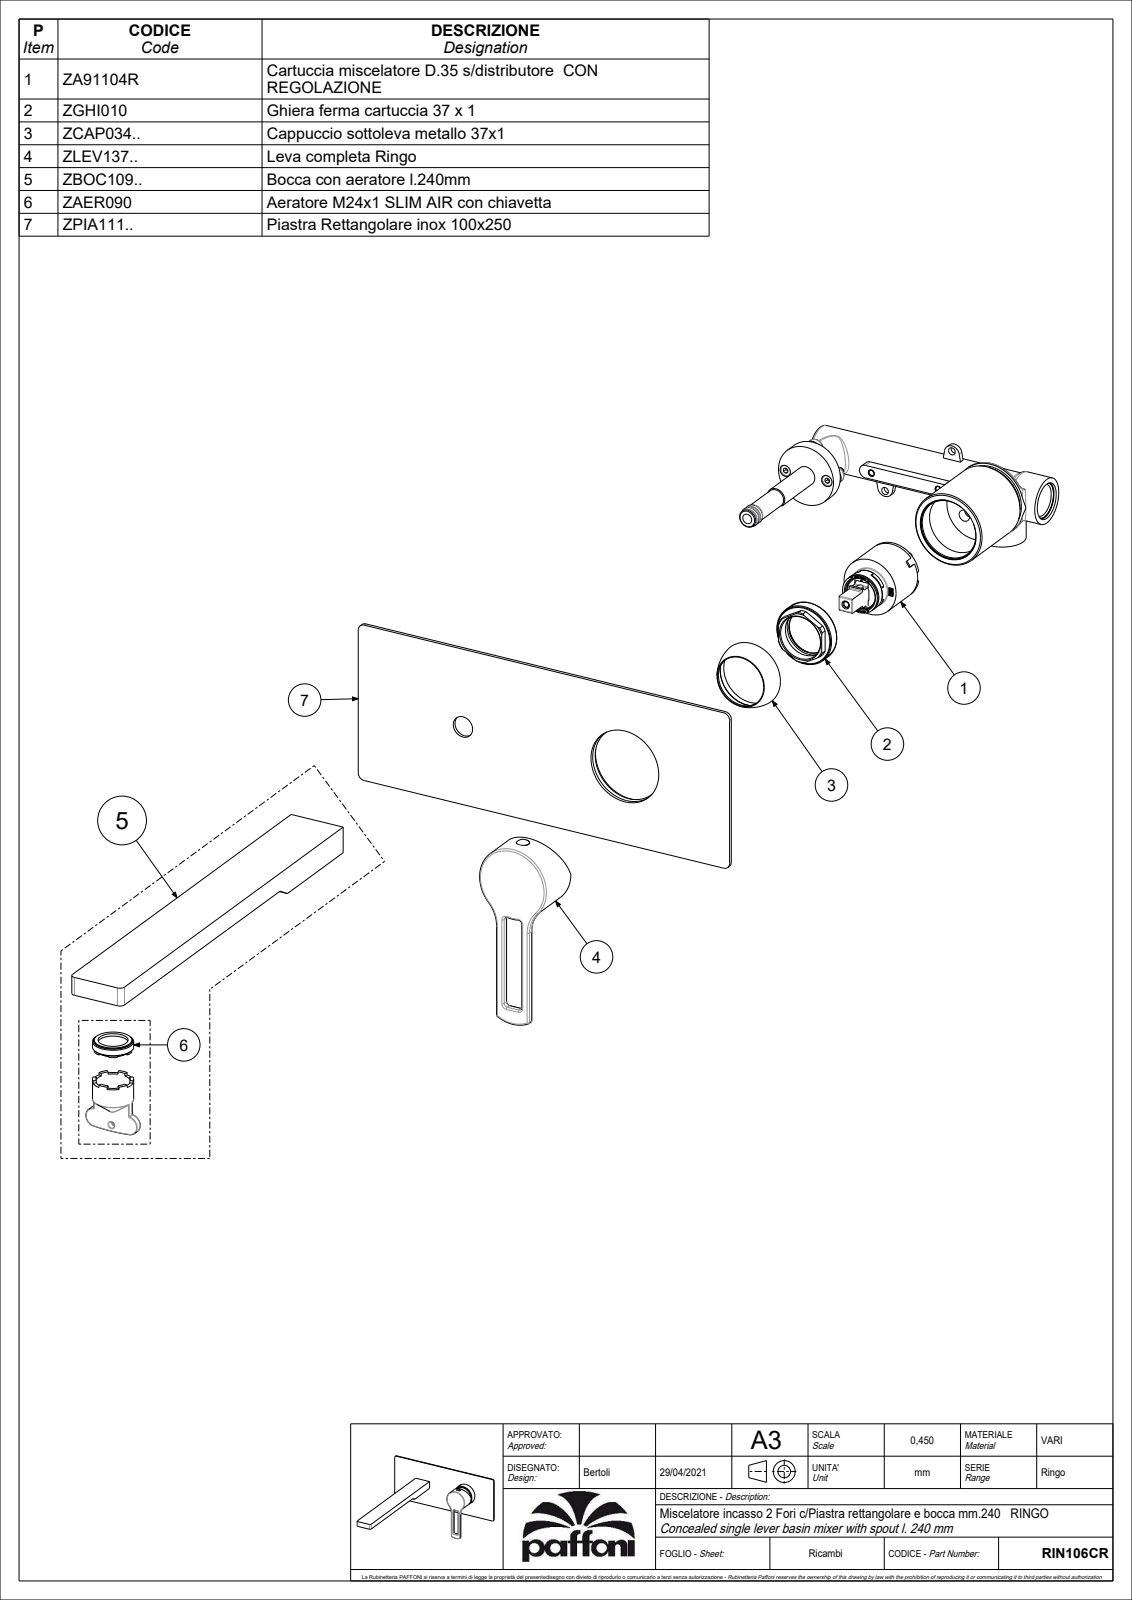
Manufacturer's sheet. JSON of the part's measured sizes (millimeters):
{"part_name": "RIN106CR", "step_written_by": "CREO PARAMETRIC BY PTC INC, 2020044 (CONFIG_CONTROL_DESIGN)", "units": "millimeters", "bodies": {"solids": 3, "faces": 1115, "planar": 616, "cylindrical": 267, "other": 232}, "overall_size": [260, 250, 140], "volume_mm3": 190818, "surface_area_mm2": 113638, "round_holes": [[4, 2], [6, 2], [3, 1], [3.3, 1], [5, 1], [7.8, 1], [11, 1], [12, 1], [13, 1], [15, 1], [17, 1], [17.5, 1]], "round_bosses_or_shafts": [[44.8, 1], [35, 1], [23.5, 1], [23.4, 1], [21.8, 1], [18.5, 1], [10.8, 1], [7.7, 1]], "partial_cylinders_radius": [[0.5, 14], [1, 14], [0.15, 11], [0.3, 4], [2, 4], [4, 4], [2.1, 2], [2.5, 2]], "face_to_face_distances": [2, 11.5, 35, 5, 16.5, 46.6, 44.6, 1.5, 1, 41.75], "hole_center_spacings": [11, 109, 232.97, 242.75]}
